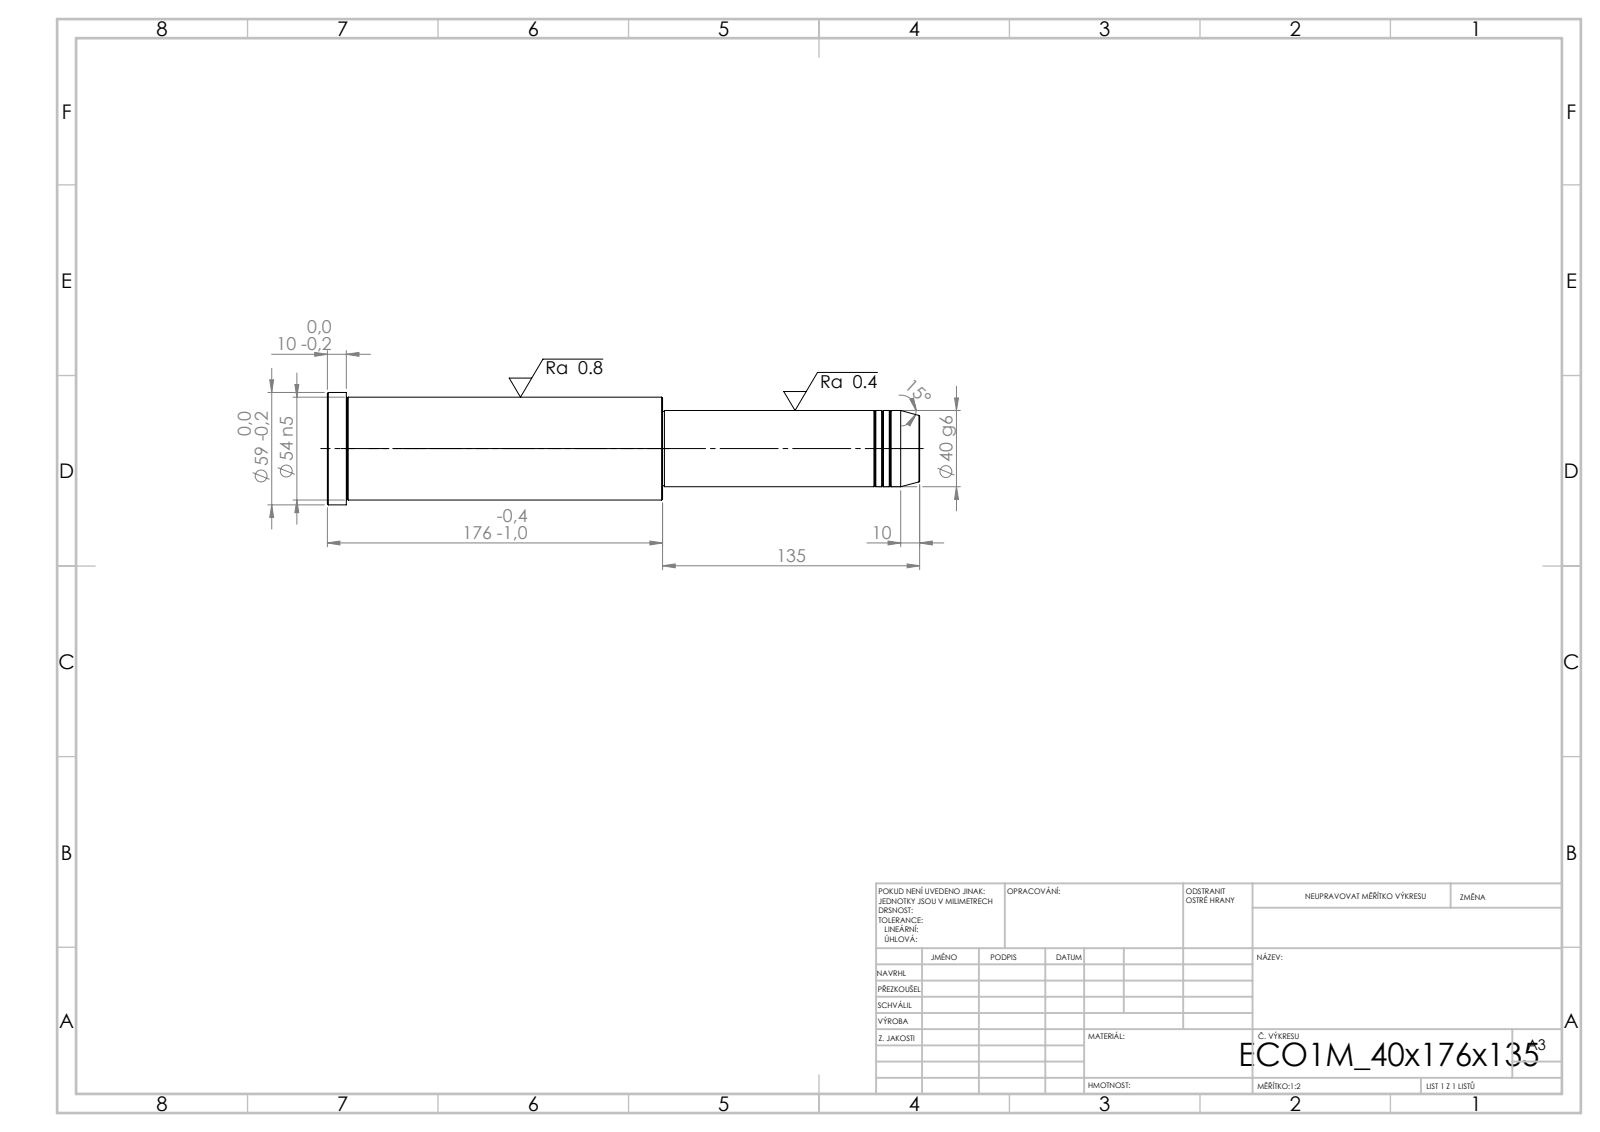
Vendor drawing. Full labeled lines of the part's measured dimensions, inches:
STEP written by: SolidWorks 2019 (CONFIG_CONTROL_DESIGN)
Units: inches
Bodies: 1 solid, 43 faces (5 planar, 14 cylindrical, 24 other)
Overall size (bounding box): 12.244 × 2.323 × 2.323
Volume: 35.1 in³ · Surface area: 81.21 in²
Round bosses / shafts (diameter × count): ⌀2.323 ×1, ⌀2.126 ×1, ⌀1.575 ×1, ⌀1.535 ×1
Main face-to-face distances: 6.929, 5.315, 12.244, 11.85, 6.535, 0.394, 5.276, 0.039, 6.575, 6.969
